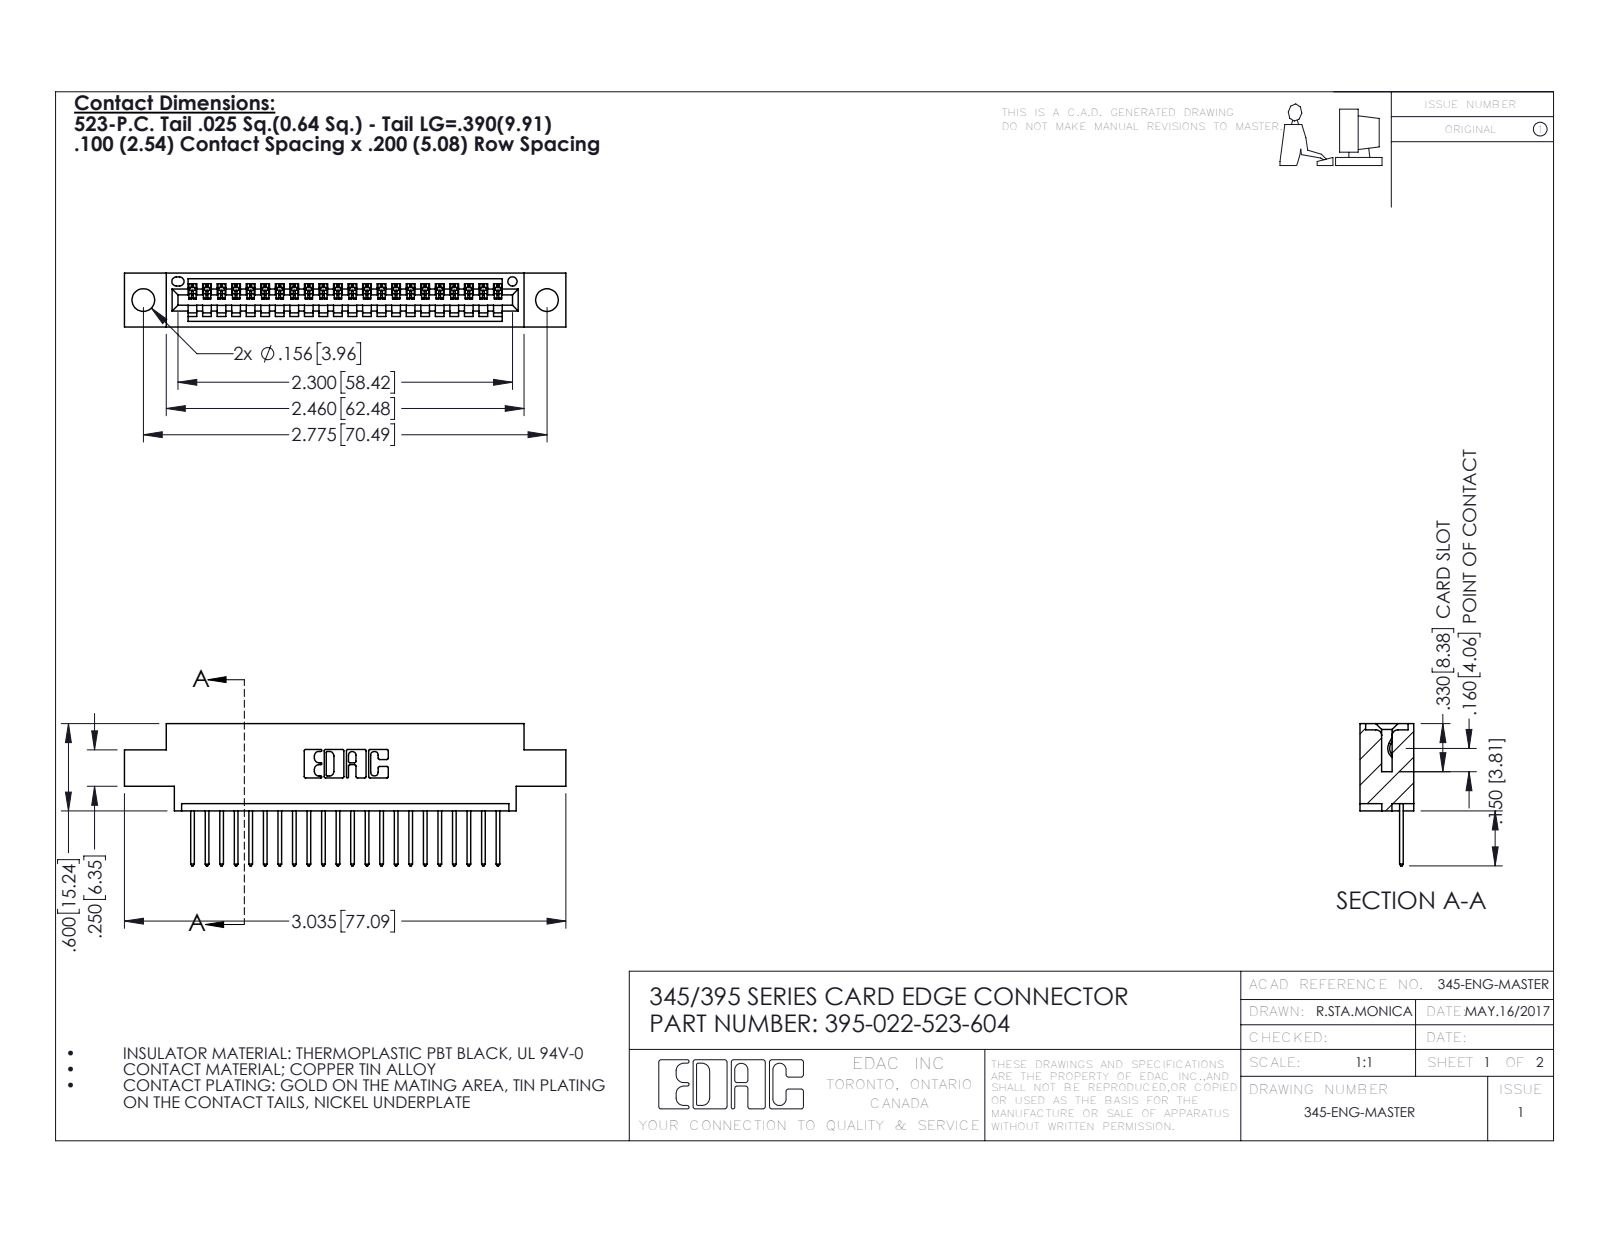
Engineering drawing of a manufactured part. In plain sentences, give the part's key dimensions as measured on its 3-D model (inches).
The part is named "345-292-001_345-293-123; 345 Part_0.170 Offset - 0.156 Dia-TH; 395-022-523-604". Its 3-D file was written by "SolidWorks 2016 (CONFIG_CONTROL_DESIGN)". It is 23 solids with 1406 faces: 964 planar, 442 cylindrical and 0 other. Overall it measures 3.035 by 0.977 by 0.37 inches. Its volume is 0.424 cubic inches and its surface area 13.83 square inches. Round holes: 2 of diameter 0.156, 1 of diameter 0.064. Partial cylindrical surfaces (rounded edges, fillets, slot ends): 44 of radius 0.006, 44 of radius 0.01, 22 of radius 0.01, 6 of radius 0.007, 6 of radius 0.031, 3 of radius 0.026, 2 of radius 0.031, 2 of radius 0.04. The main face-to-face distances are 0.072, 0.298, 0.37, 0.2, 0.098, 0.272, 0.025, 0.225, 0.175, 0.15. The hole center spacings are 0.27, 2.541, 2.775.
